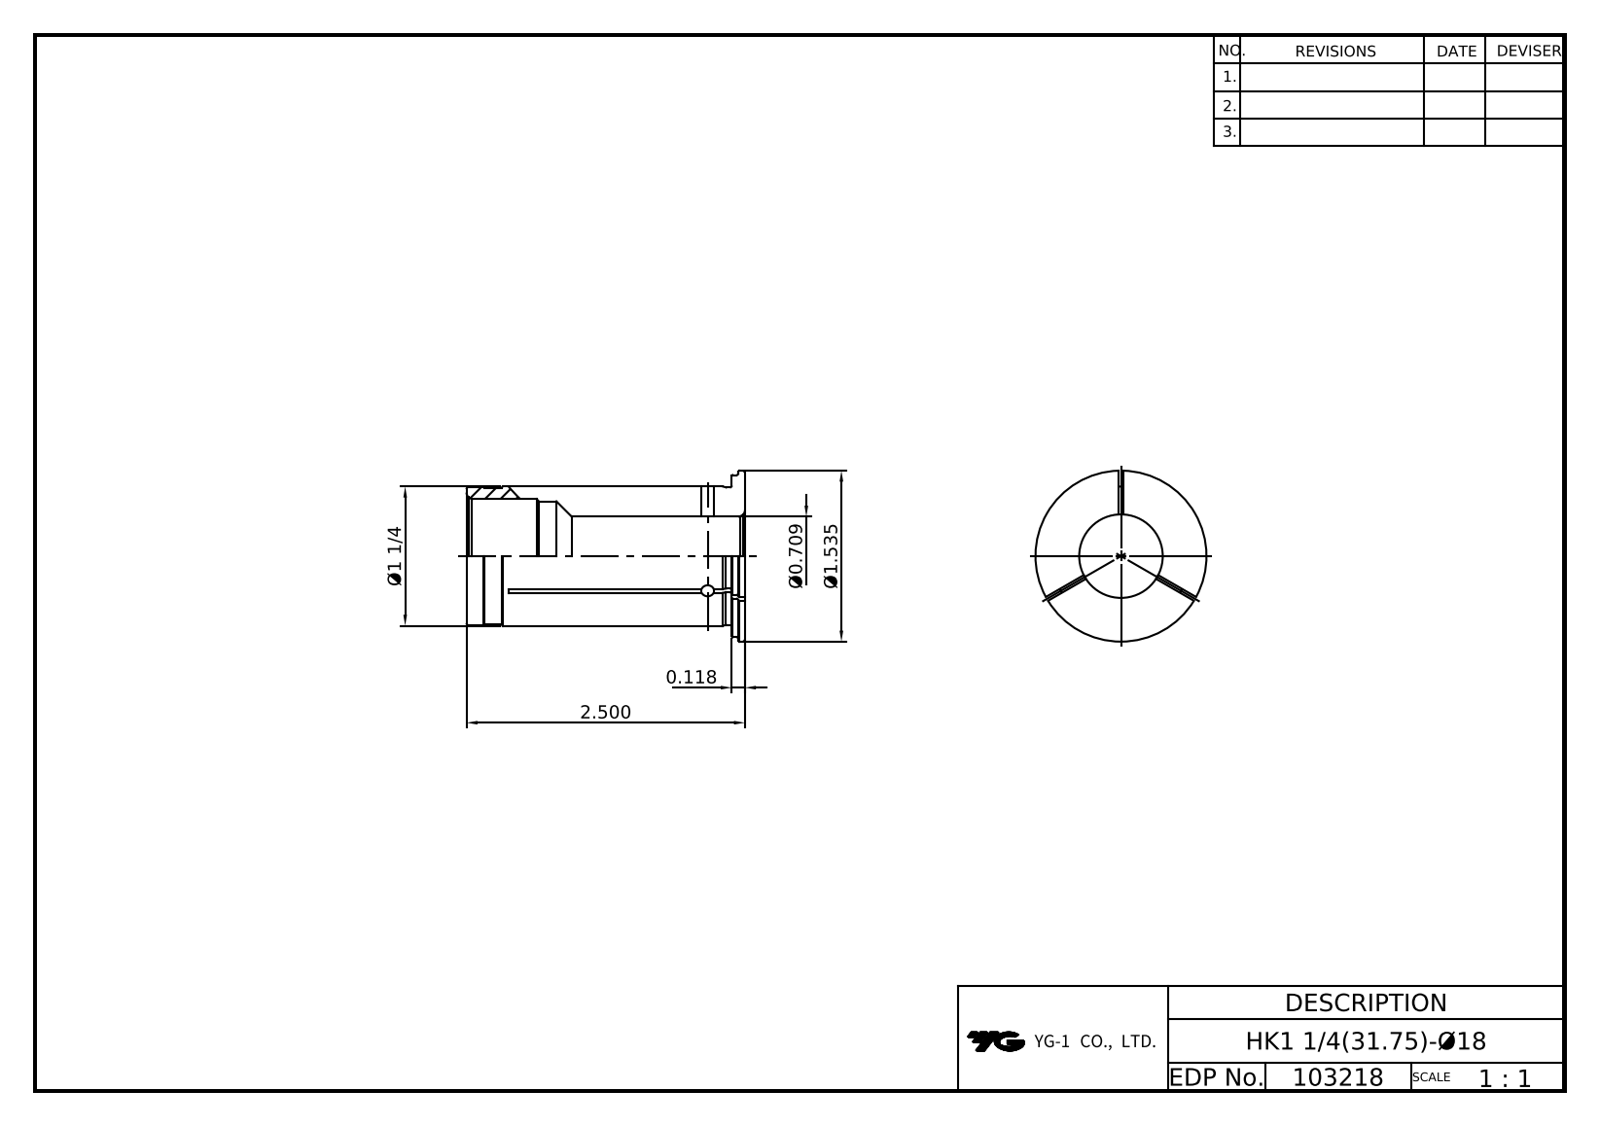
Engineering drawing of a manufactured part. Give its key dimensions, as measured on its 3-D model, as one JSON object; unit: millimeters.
{"part_name": "LO-HK31.75-18", "step_written_by": "Autodesk Inventor 2025 (AP242_MANAGED_MODEL_BASED_3D_ENGINEERING_MIM_LF)", "units": "millimeters", "bodies": {"solids": 1, "faces": 16, "planar": 4, "cylindrical": 6, "other": 6}, "overall_size": [63.5, 39, 39], "volume_mm3": 29252, "surface_area_mm2": 12173, "round_holes": [[18, 1], [25, 1], [26, 1]], "round_bosses_or_shafts": [[39, 1], [37, 1], [31.75, 1]], "face_to_face_distances": [63.5, 60.5, 3, 1.5, 62]}
